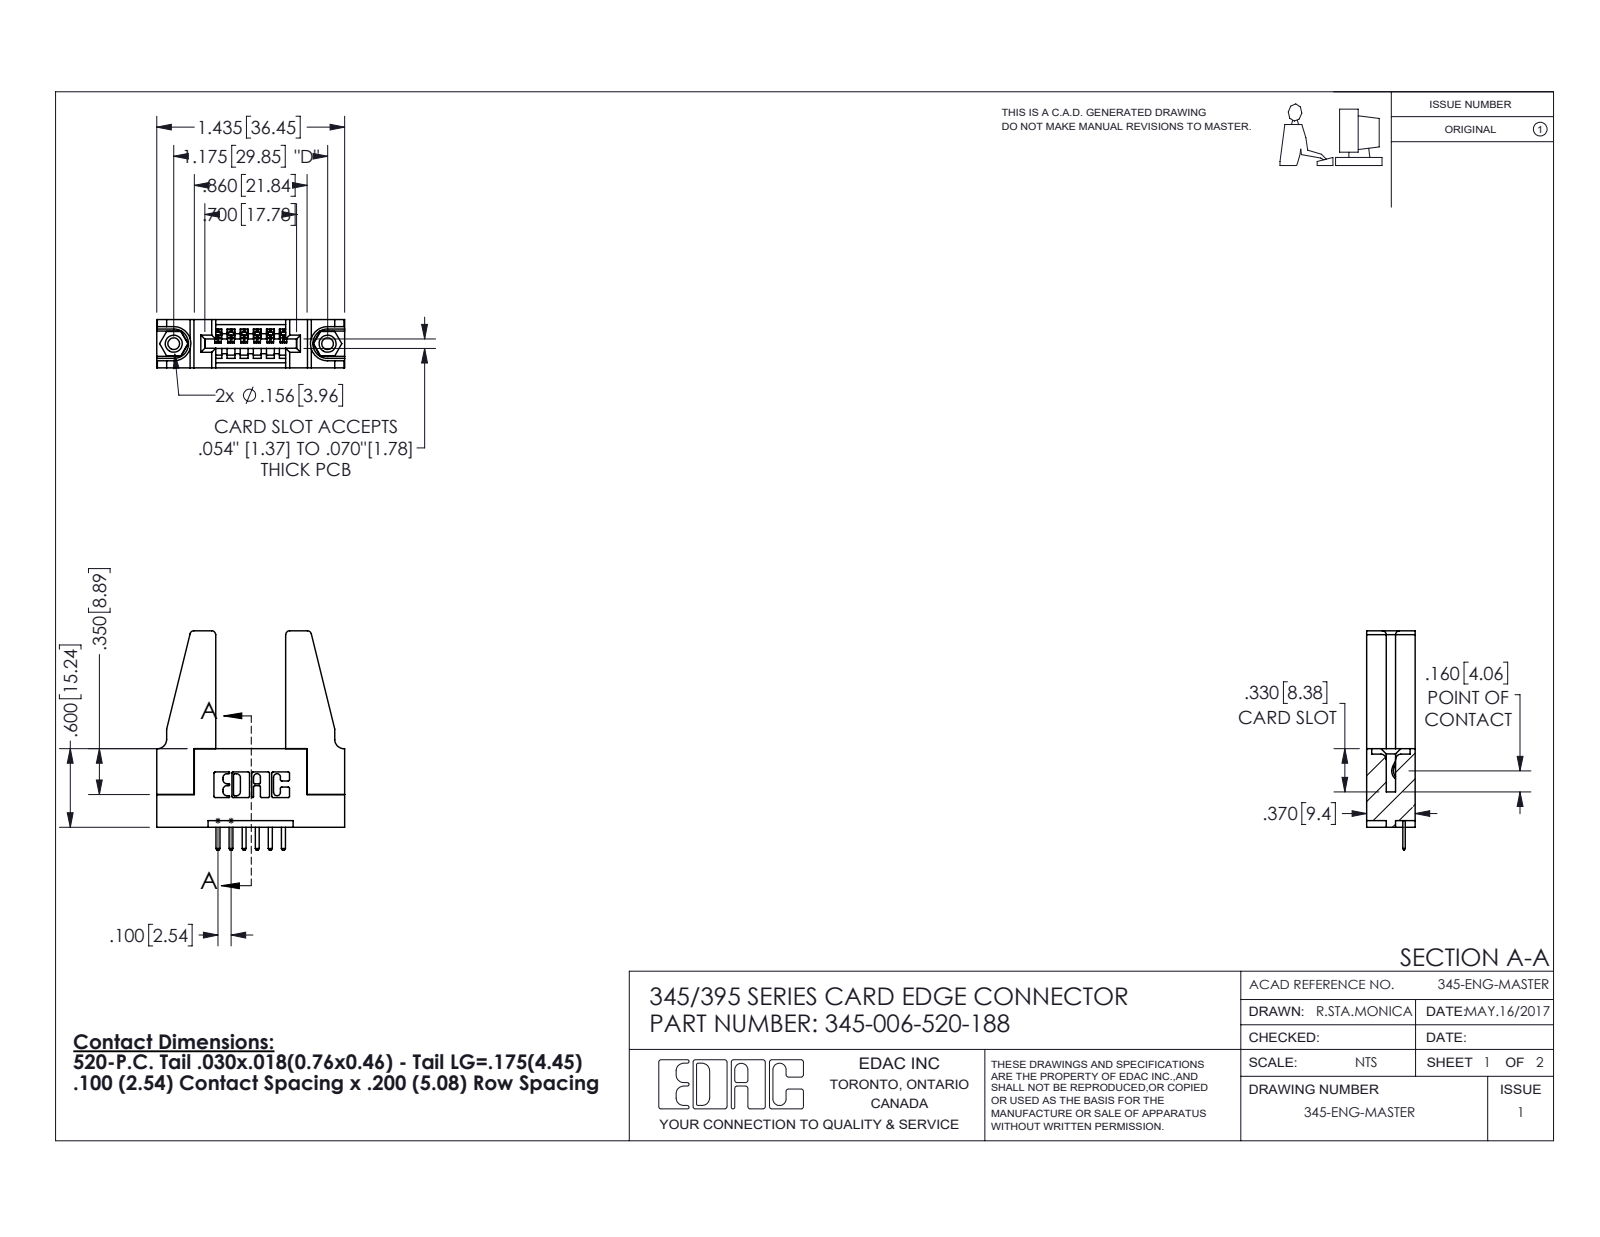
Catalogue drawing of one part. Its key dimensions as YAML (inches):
part_name: "345-250-001_345-250-001-102; 345 Part_Flush Mounting Lugs - 0.156 Dia-TH; 345-006-520-188; 345-292-001_345-293-120 (+1 more)"
step_written_by: "SolidWorks 2016 (CONFIG_CONTROL_DESIGN)"
units: inches
bodies: {solids: 11, faces: 622, planar: 404, cylindrical: 202, other: 16}
overall_size: [1.675, 1.436, 0.37]
volume: 0.391
surface_area: 10.5
round_holes:
  - {diameter: 0.089, count: 2}
  - {diameter: 0.125, count: 2}
  - {diameter: 0.156, count: 2}
  - {diameter: 0.064, count: 1}
round_bosses_or_shafts:
  - {diameter: 0.155, count: 2}
partial_cylinders:
  - {radius: 0.01, count: 22}
  - {radius: 0.01, count: 14}
  - {radius: 0.006, count: 12}
  - {radius: 0.03, count: 8}
  - {radius: 0.007, count: 6}
  - {radius: 0.031, count: 6}
  - {radius: 0.026, count: 3}
  - {radius: 0.031, count: 2}
face_to_face_distances: [0.37, 0.2, 0.072, 0.298, 0.698, 0.15, 0.148, 0.35, 0.25, 0.077]
hole_center_spacings: [0.27, 0.946, 1.175]
